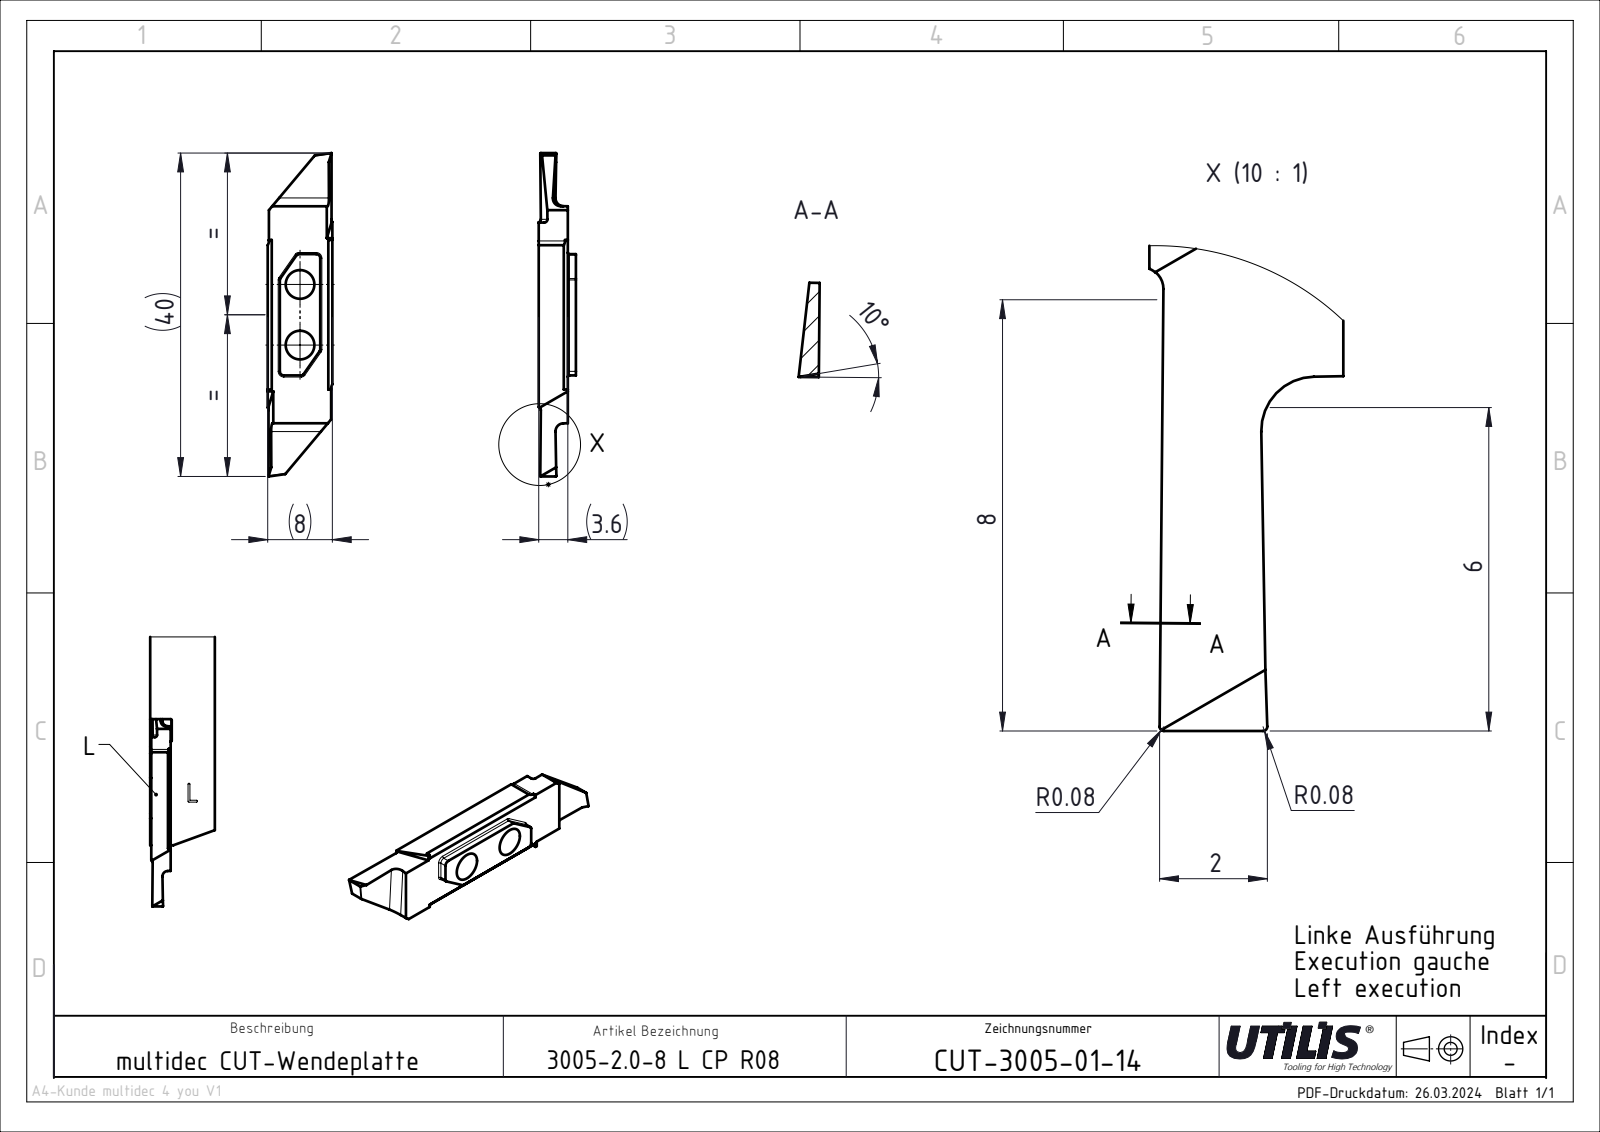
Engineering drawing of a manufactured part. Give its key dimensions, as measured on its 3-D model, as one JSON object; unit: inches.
{"part_name": "CUT-3005 CP; ASME Y14.5", "step_written_by": "SolidWorks 2023 SP4 || FormatWorks Professional (AP242_MANAGED_MODEL_BASED_3D_ENGINEERING_MIM_LF)", "units": "inches", "bodies": {"solids": 1, "faces": 36, "planar": 22, "cylindrical": 14, "other": 0}, "overall_size": [1.575, 0.315, 0.142], "volume_in3": 0.049, "surface_area_in2": 1.33, "round_holes": [[0.14, 2]], "partial_cylinders_radius": [[0.039, 4], [0.016, 2]], "face_to_face_distances": [0.142, 0.315, 0.309, 0.887, 0.303, 1.575, 0.423, 1.152, 0.728], "hole_center_spacings": [0.295]}
